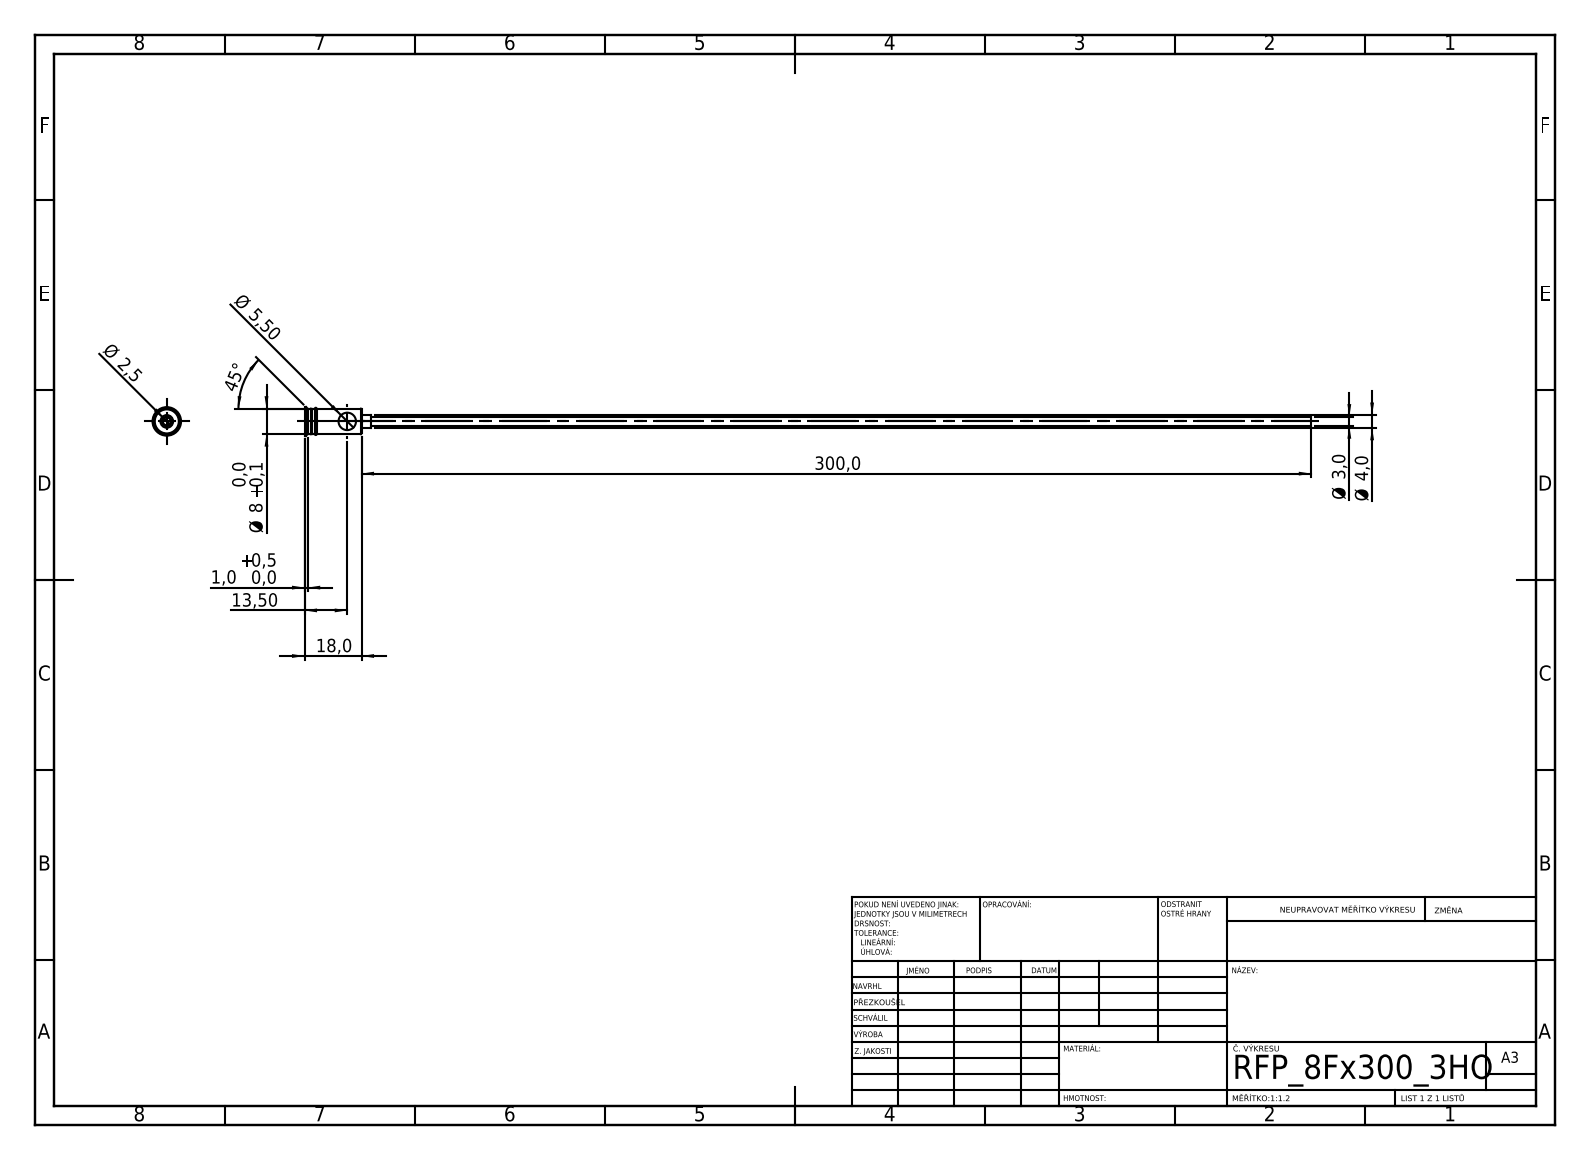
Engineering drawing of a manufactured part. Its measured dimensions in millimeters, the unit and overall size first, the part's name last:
Units: millimetres
Overall size (bounding box): 318 × 9 × 9
Round holes (diameter × count): ⌀2.5 ×1, ⌀5.5 ×1
Round bosses / shafts (diameter × count): ⌀9 ×1, ⌀8 ×1, ⌀4 ×1, ⌀3 ×1
Main face-to-face distances: 18, 3.4, 16, 2, 15.7, 2.3, 3, 18.7, 19, 21
Volume: 1 374 mm³ · Surface area: 5 881 mm²
Bodies: 1 solid, 44 faces (20 planar, 16 cylindrical, 8 other)
STEP written by: SolidWorks 2019 (CONFIG_CONTROL_DESIGN)
